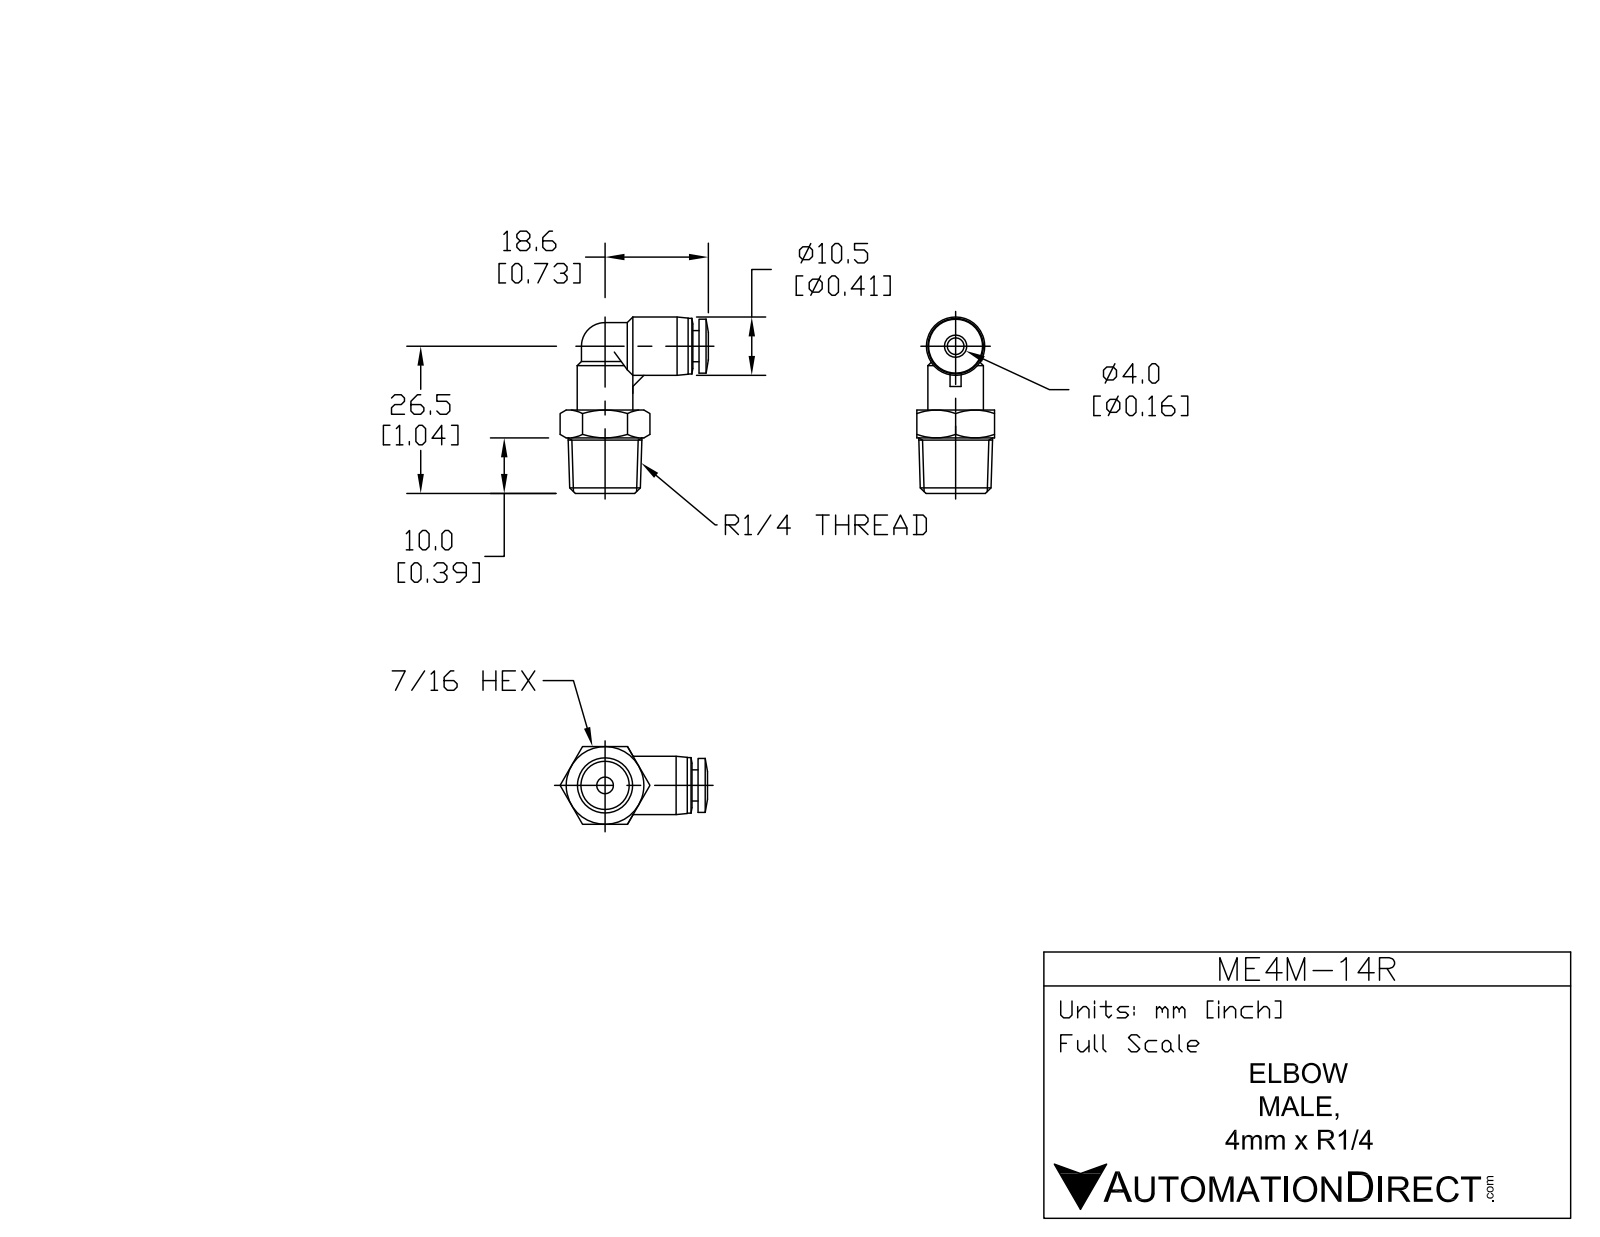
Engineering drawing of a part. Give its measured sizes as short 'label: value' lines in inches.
name: ME4M-14R
written by: SolidWorks 2015 (AUTOMOTIVE_DESIGN)
unit: in
bodies: 1 solid, 69 faces (17 planar, 19 cylindrical, 33 other)
size: 1.25 × 1.045 × 0.551
volume: 0.237 in³; area: 3.698 in²
holes: 2× ⌀0.118, 1× ⌀0.169
bosses: 2× ⌀0.394, 1× ⌀0.413, 1× ⌀0.382, 1× ⌀0.22
rounds: 2× R0.167
face distances: 0.551, 0.591, 0.043, 0.394, 0.197, 0.472, 0.516, 0.236, 0.315, 0.079
